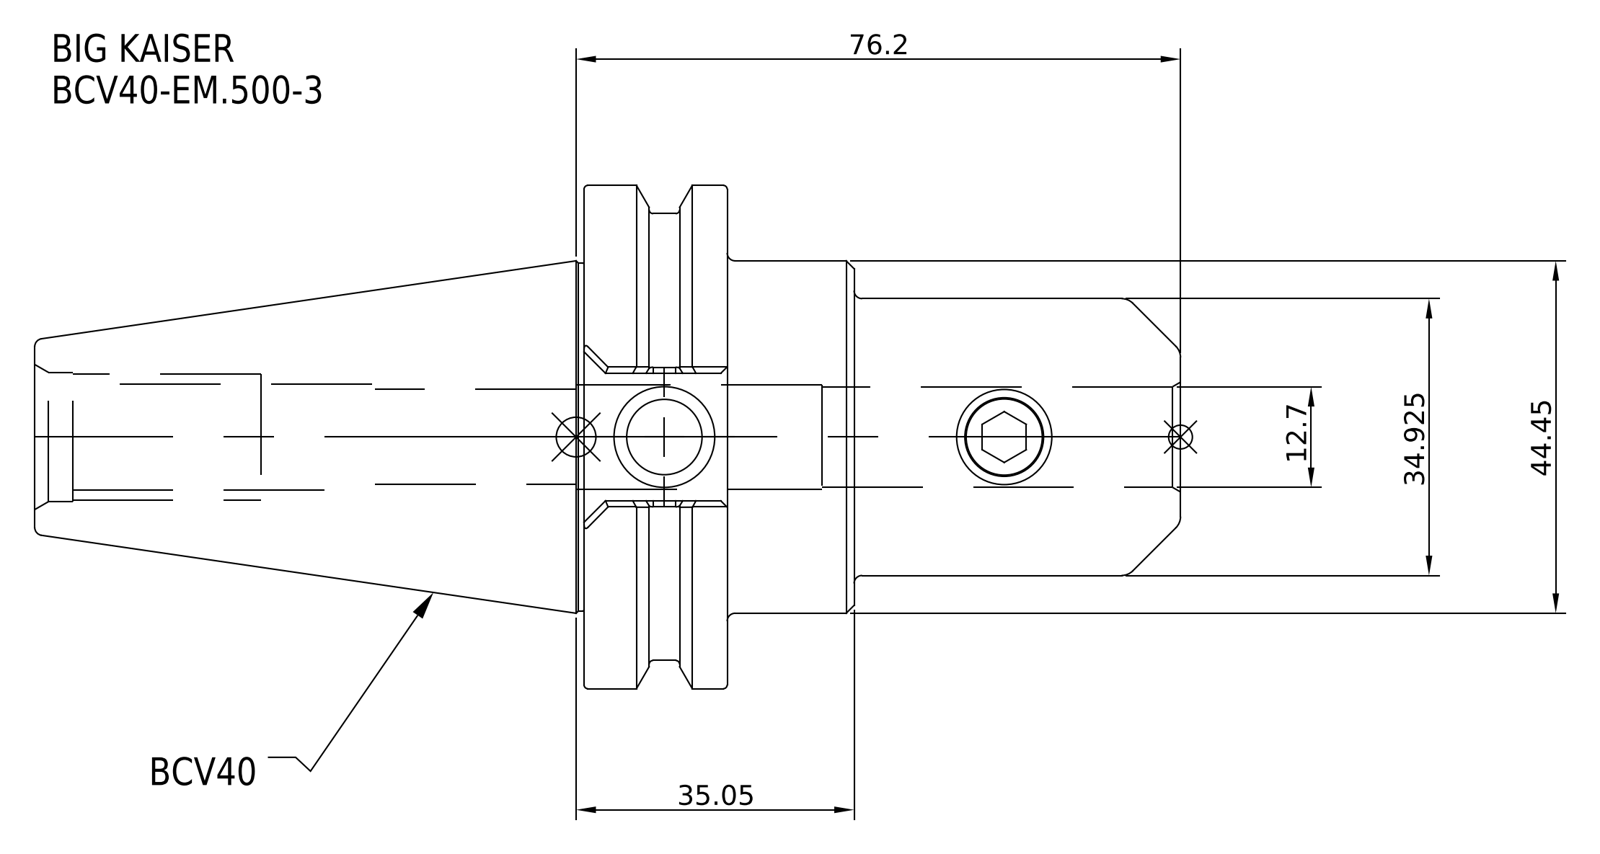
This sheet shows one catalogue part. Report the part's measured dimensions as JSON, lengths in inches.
{"part_name": "BCV40-EM_500-3", "step_written_by": "SolidWorks 2021 (CONFIG_CONTROL_DESIGN)", "units": "inches", "bodies": {"solids": 1, "faces": 30, "planar": 8, "cylindrical": 14, "other": 8}, "overall_size": [5.687, 2.5, 2.5], "volume_in3": 10.85, "surface_area_in2": 39, "round_holes": [[0.5, 1]], "round_bosses_or_shafts": [[2.5, 1], [2.219, 1], [1.75, 1], [1.375, 1]], "face_to_face_distances": [0.711, 0.63, 1.341, 4.067, 3.437, 2.726, 1.62, 2.25, 2.961, 5.687]}
